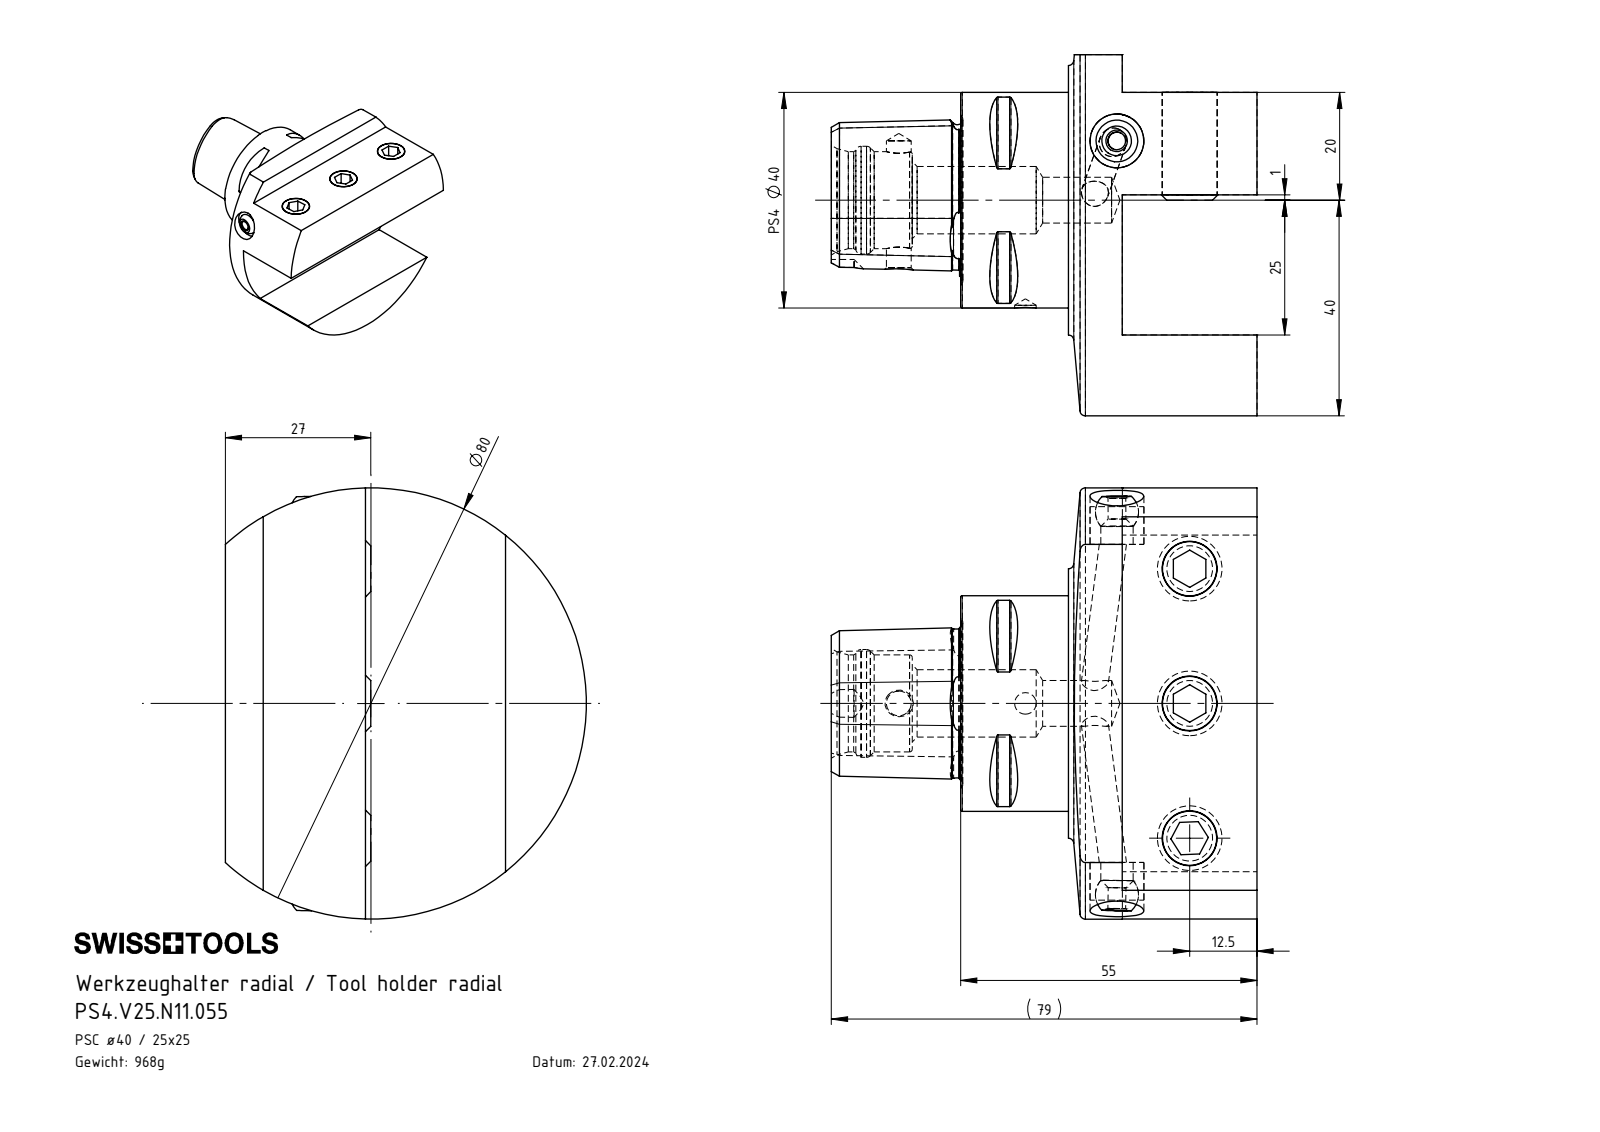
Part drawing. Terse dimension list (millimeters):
name: PS4-V25.N11.055_A; KU1-U10.001.010; PS4.V25.N11.055; KU1-U10.001.010_1 (+2 more)
written by: SolidWorks 2022 (AUTOMOTIVE_DESIGN)
unit: mm
bodies: 8 solids, 245 faces (62 planar, 66 cylindrical, 117 other)
size: 80 × 79 × 67
volume: 123 846 mm³; area: 33 143 mm²
holes: 3× ⌀10.2, 2× ⌀3.3, 2× ⌀5, 1× ⌀4, 1× ⌀4.6, 1× ⌀6, 1× ⌀8.5, 1× ⌀10, 1× ⌀12.5, 1× ⌀18, 1× ⌀20
bosses: 3× ⌀12, 1× ⌀40
rounds: 8× R0.3, 1× R3, 1× R40
face distances: 25, 26, 19, 45, 10, 35, 20, 7, 52, 30
hole spacings: 25, 39.44, 59.51, 23.5, 30.5, 50, 54
